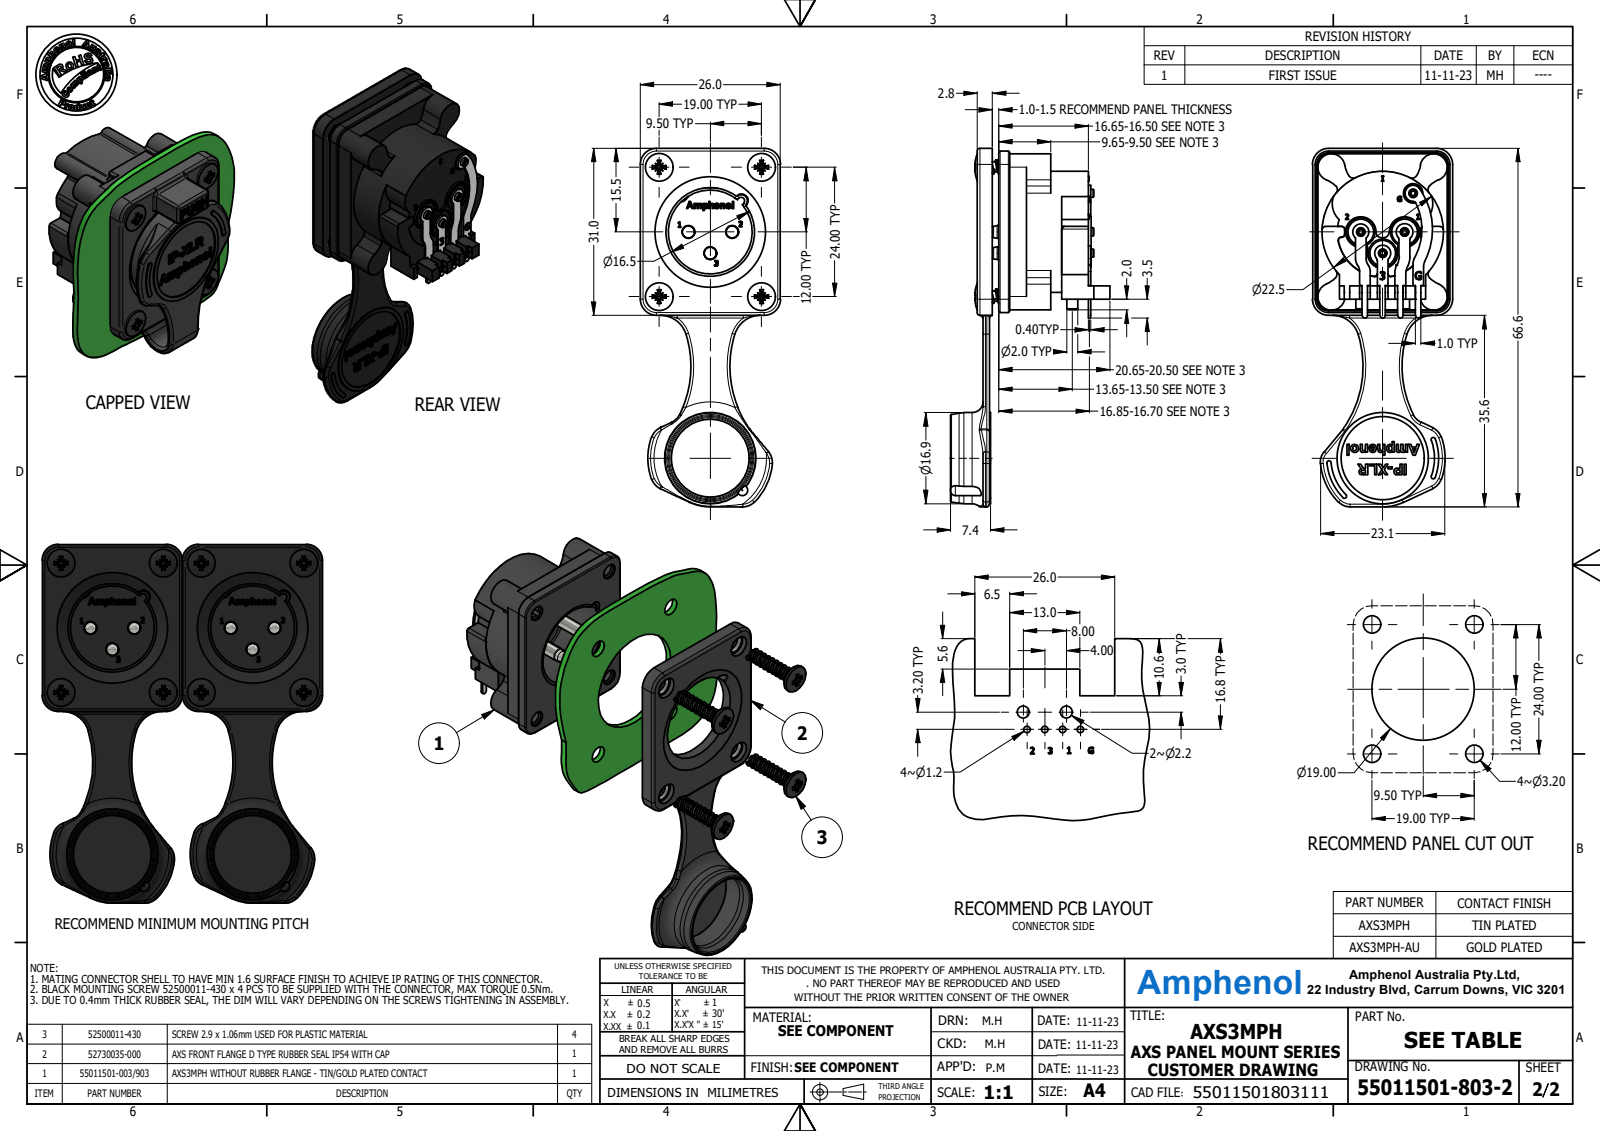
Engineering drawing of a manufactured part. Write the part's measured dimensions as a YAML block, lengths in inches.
part_name: "AXS3MPH"
step_written_by: "Autodesk Inventor 2022 (AUTOMOTIVE_DESIGN)"
units: inches
bodies: {solids: 1, faces: 2247, planar: 608, cylindrical: 486, other: 1153}
overall_size: [2.62, 1.165, 1.024]
volume: 0.575
surface_area: 13.92
round_holes:
  - {diameter: 0.094, count: 7}
  - {diameter: 0.031, count: 4}
  - {diameter: 0.063, count: 4}
  - {diameter: 0.116, count: 4}
  - {diameter: 0.134, count: 4}
  - {diameter: 0.157, count: 4}
  - {diameter: 0.115, count: 3}
  - {diameter: 0.187, count: 3}
  - {diameter: 0.087, count: 1}
  - {diameter: 0.102, count: 1}
  - {diameter: 0.142, count: 1}
  - {diameter: 0.567, count: 1}
round_bosses_or_shafts:
  - {diameter: 0.059, count: 4}
  - {diameter: 0.112, count: 3}
  - {diameter: 0.093, count: 3}
  - {diameter: 0.079, count: 2}
  - {diameter: 0.886, count: 1}
  - {diameter: 0.669, count: 1}
  - {diameter: 0.665, count: 1}
  - {diameter: 0.134, count: 1}
partial_cylinders:
  - {radius: 0.02, count: 41}
  - {radius: 0.039, count: 14}
  - {radius: 0.016, count: 12}
  - {radius: 0.045, count: 12}
  - {radius: 0.079, count: 11}
  - {radius: 0.118, count: 10}
  - {radius: 0.197, count: 10}
  - {radius: 0.01, count: 8}
face_to_face_distances: [0.047, 0.069, 0.022, 0.157, 0.089, 0.11, 0.116, 0.041, 0.813, 0.449]
hole_center_spacings: [0.519, 0.603, 0.713, 0.16, 0.223, 0.49, 0.731, 0.748]
